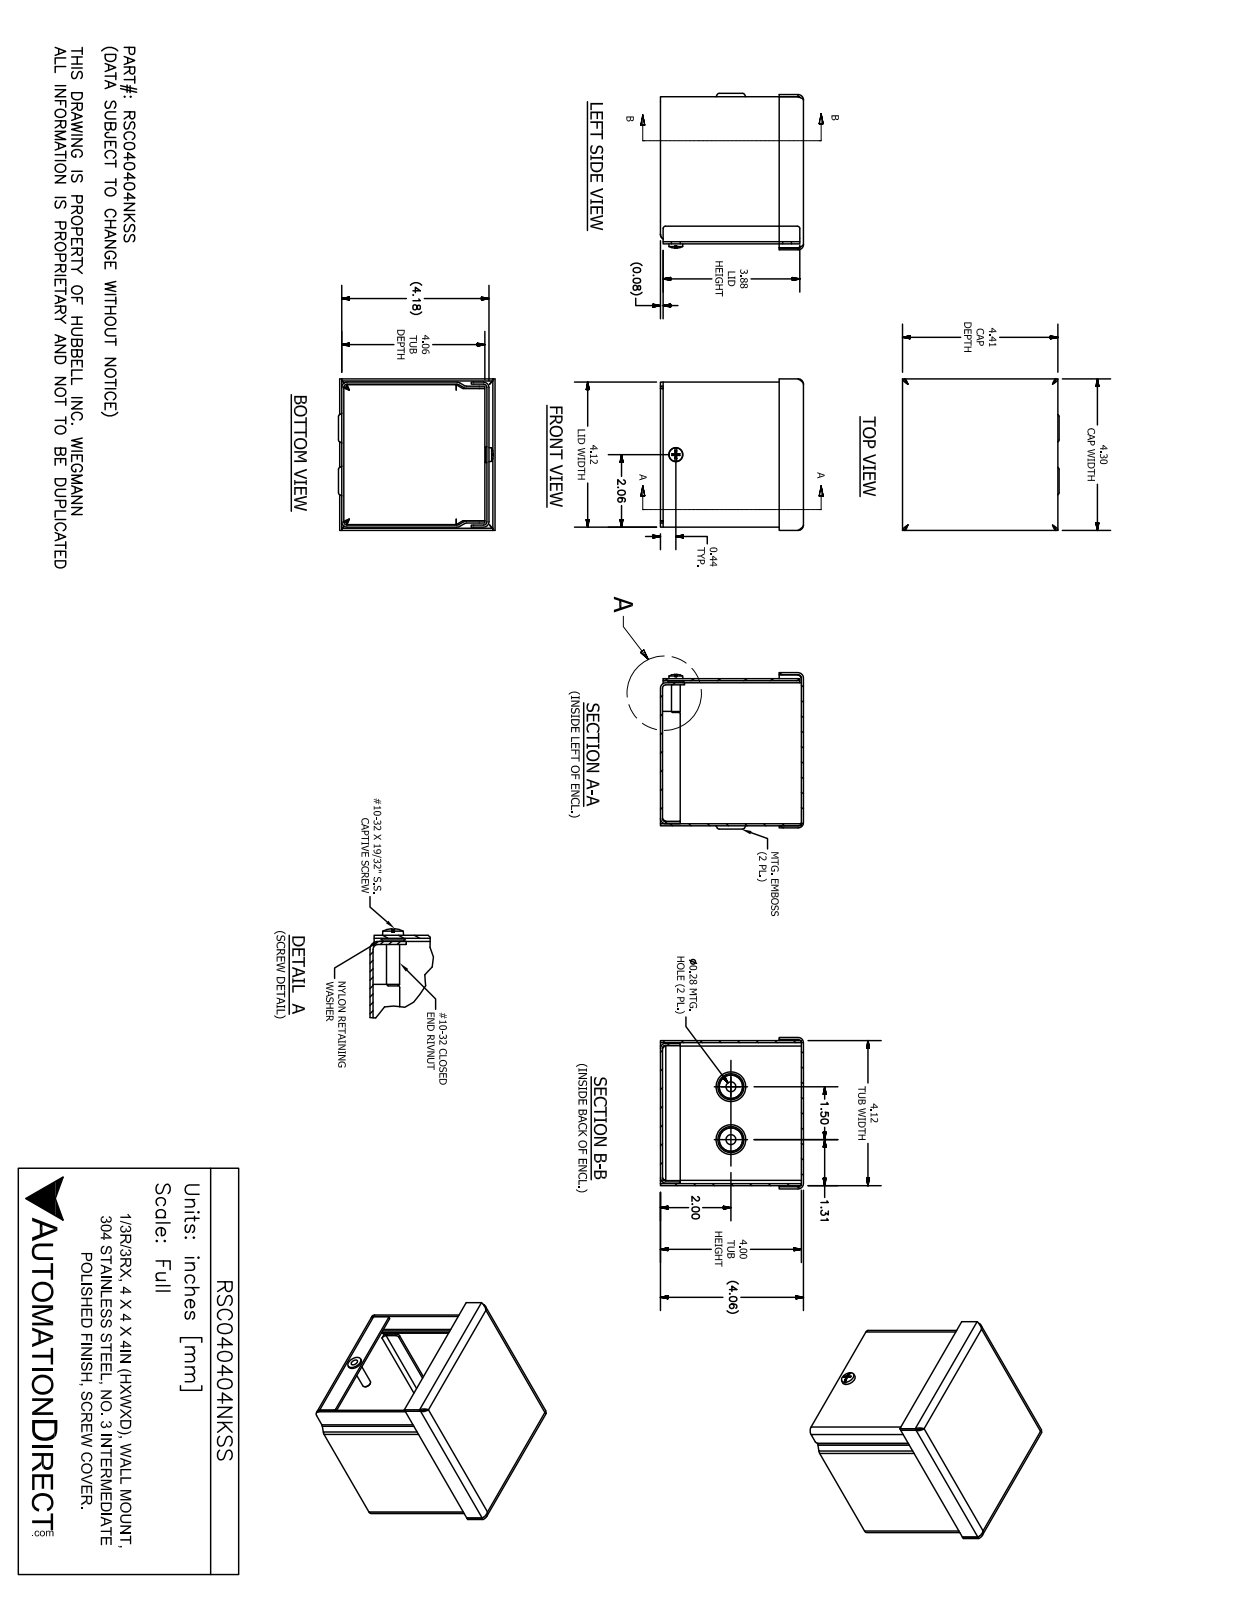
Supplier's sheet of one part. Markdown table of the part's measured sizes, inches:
| quantity | value |
| --- | --- |
| part name | RSC040404NKSS |
| STEP written by | SolidWorks 2017 (AUTOMOTIVE_DESIGN) |
| units | inches |
| bodies | 7 solids, 231 faces (124 planar, 58 cylindrical, 49 other) |
| overall size | 4.441 × 4.299 × 4.059 |
| volume | 7.04 in³ |
| surface area | 244.8 in² |
| round holes (diameter × count) | 0.25 × 2, 0.281 × 2, 0.156 × 1, 0.196 × 1, 0.257 × 1, 0.278 × 1 |
| round bosses / shafts (diameter × count) | 0.453 × 1, 0.406 × 1, 0.248 × 1, 0.167 × 1 |
| partial cylindrical surfaces (radius × count) | 0.094 × 16, 0.153 × 16, 0.031 × 2, 0.062 × 2, 0.063 × 2, 0.089 × 1, 0.156 × 1 |
| main face-to-face distances | 0.059, 4.059, 4, 4.117, 4.176, 4.118, 3.941, 4.058, 0.09, 4.149 |
| hole center spacings | 1.733, 1.761, 1.5, 3.156 |
